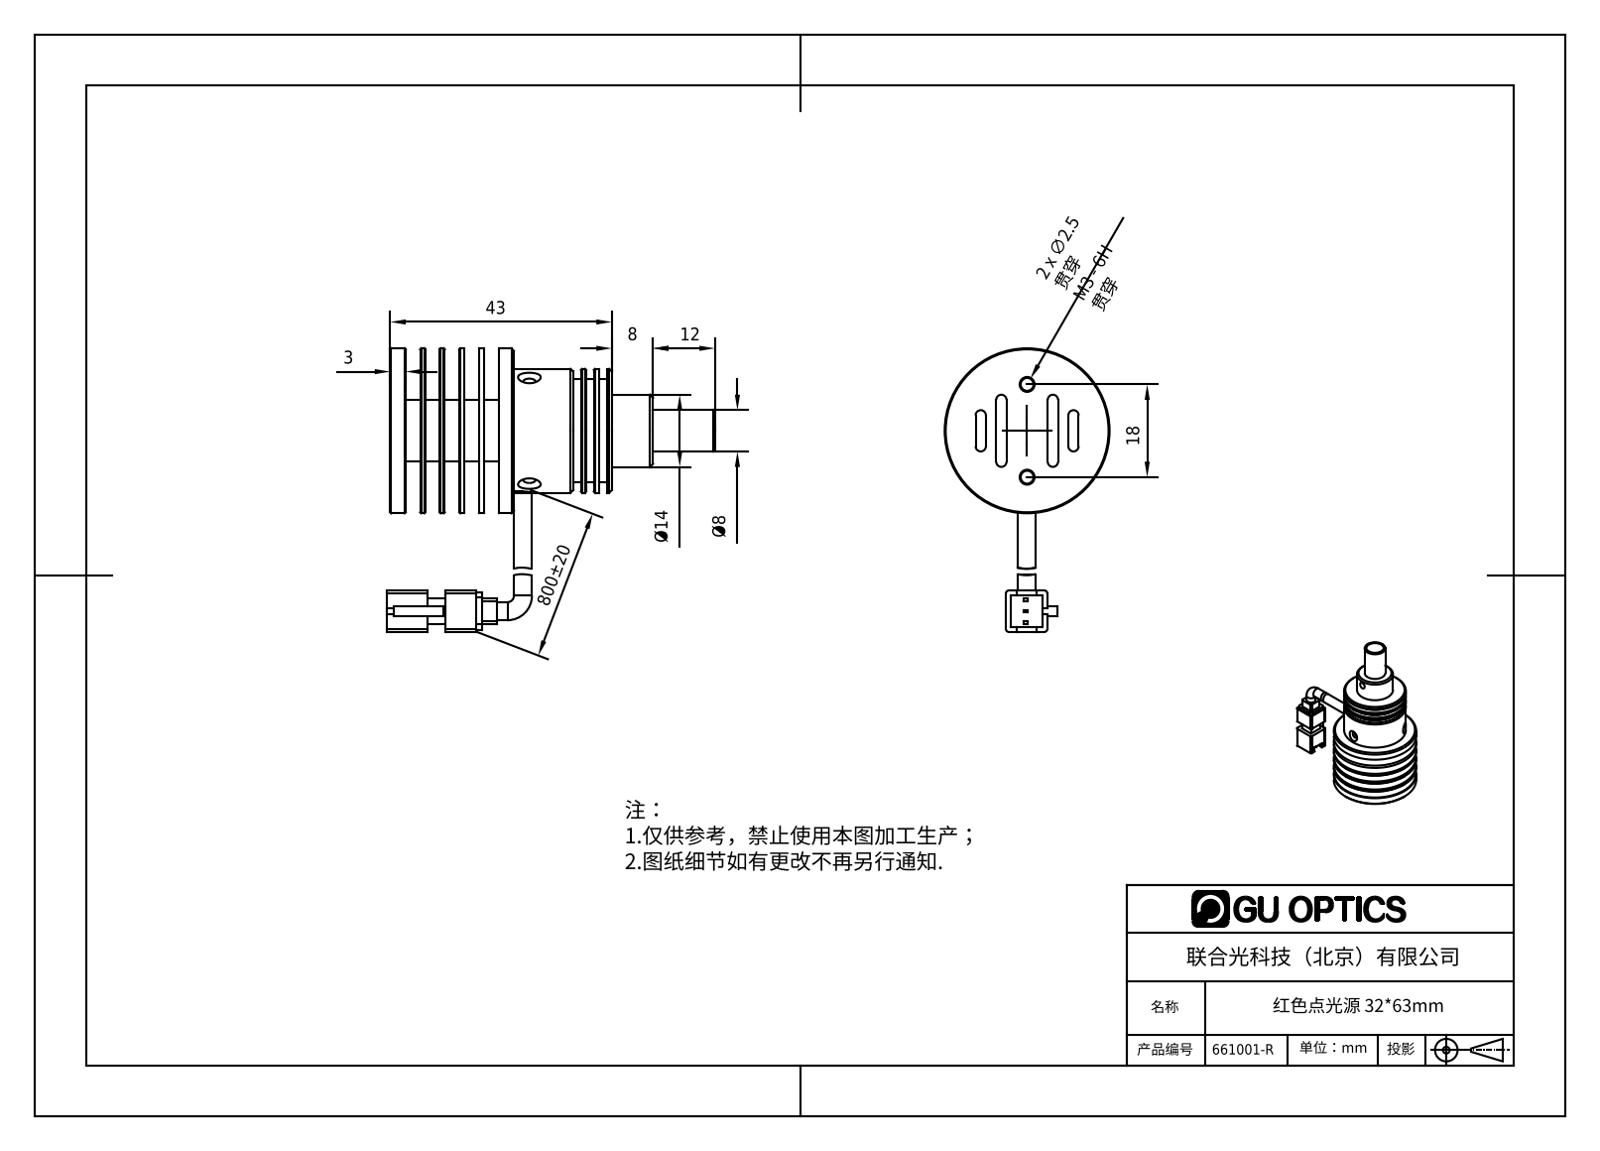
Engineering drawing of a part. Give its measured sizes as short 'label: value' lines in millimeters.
name: 661001
written by: SolidWorks 2016 (AUTOMOTIVE_DESIGN)
unit: mm
bodies: 10 solids, 401 faces (157 planar, 168 cylindrical, 76 other)
size: 63.75 × 55 × 32
volume: 17 724 mm³; area: 19 704 mm²
holes: 7× ⌀1.6, 3× ⌀2, 3× ⌀2.4, 3× ⌀2.5, 2× ⌀2.2, 1× ⌀6.21, 1× ⌀6.8, 1× ⌀15.8, 1× ⌀16.8, 1× ⌀19.1, 1× ⌀20.1
bosses: 2× ⌀3.5, 1× ⌀32, 1× ⌀24, 1× ⌀20, 1× ⌀17, 1× ⌀15.6, 1× ⌀14.4, 1× ⌀14
rounds: 12× R1, 8× R0.5, 3× R1.5, 1× R1.65
face distances: 3.8, 2.8, 7.6, 1, 6.6, 3.89, 7.69, 4.8, 11.49, 10.4
hole spacings: 8.49, 6, 6.37, 13.91, 9, 12.01, 6.01, 6.38
